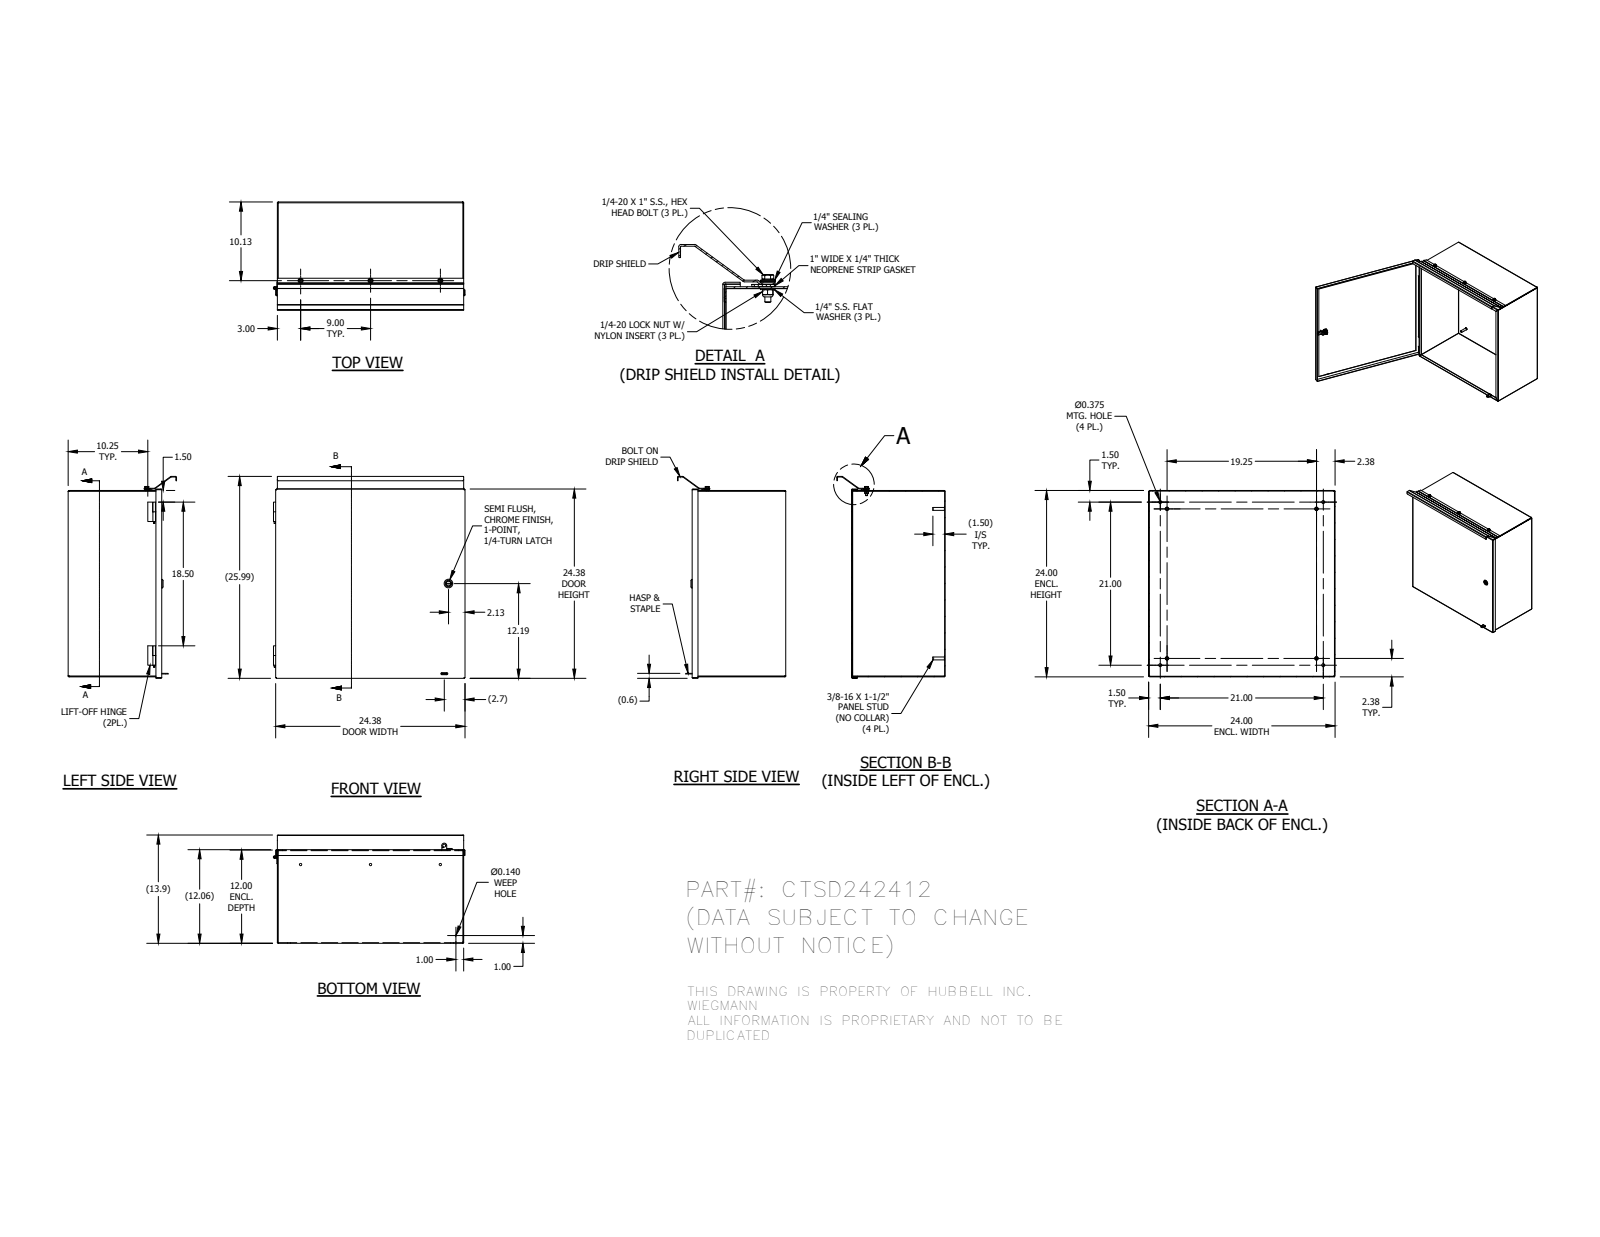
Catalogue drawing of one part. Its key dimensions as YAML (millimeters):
part_name: "CTSD242412BKP; CTSD2424DR; 31815; HC2527 (+8 more)"
step_written_by: "Autodesk Inventor 2014 (AUTOMOTIVE_DESIGN)"
units: millimeters
bodies: {solids: 36, faces: 860, planar: 456, cylindrical: 259, other: 145}
overall_size: [660.27, 626.48, 354.32]
volume: 3224000
surface_area: 3455000
round_holes:
  - {diameter: 9.52, count: 5}
  - {diameter: 4.98, count: 3}
  - {diameter: 5.97, count: 3}
  - {diameter: 6.99, count: 3}
  - {diameter: 7.14, count: 3}
  - {diameter: 7.37, count: 3}
  - {diameter: 3.17, count: 1}
  - {diameter: 3.56, count: 1}
  - {diameter: 5, count: 1}
  - {diameter: 5.36, count: 1}
  - {diameter: 5.56, count: 1}
  - {diameter: 8, count: 1}
round_bosses_or_shafts:
  - {diameter: 11.73, count: 4}
  - {diameter: 9.52, count: 4}
  - {diameter: 16.51, count: 3}
  - {diameter: 15.88, count: 3}
  - {diameter: 15.24, count: 3}
  - {diameter: 11.13, count: 3}
  - {diameter: 11.05, count: 3}
  - {diameter: 6.6, count: 3}
partial_cylinders:
  - {radius: 0.3, count: 30}
  - {radius: 0.79, count: 20}
  - {radius: 2.67, count: 18}
  - {radius: 0.5, count: 10}
  - {radius: 1.78, count: 8}
  - {radius: 3.17, count: 4}
  - {radius: 4, count: 4}
  - {radius: 0.4, count: 3}
face_to_face_distances: [1.88, 304.4, 607.72, 302.52, 306.28, 609.6, 605.84, 302.92, 1.48, 3.47]
hole_center_spacings: [533.4, 228.6, 266.96, 585.92, 754.34, 7.32, 57.12, 63.41]
